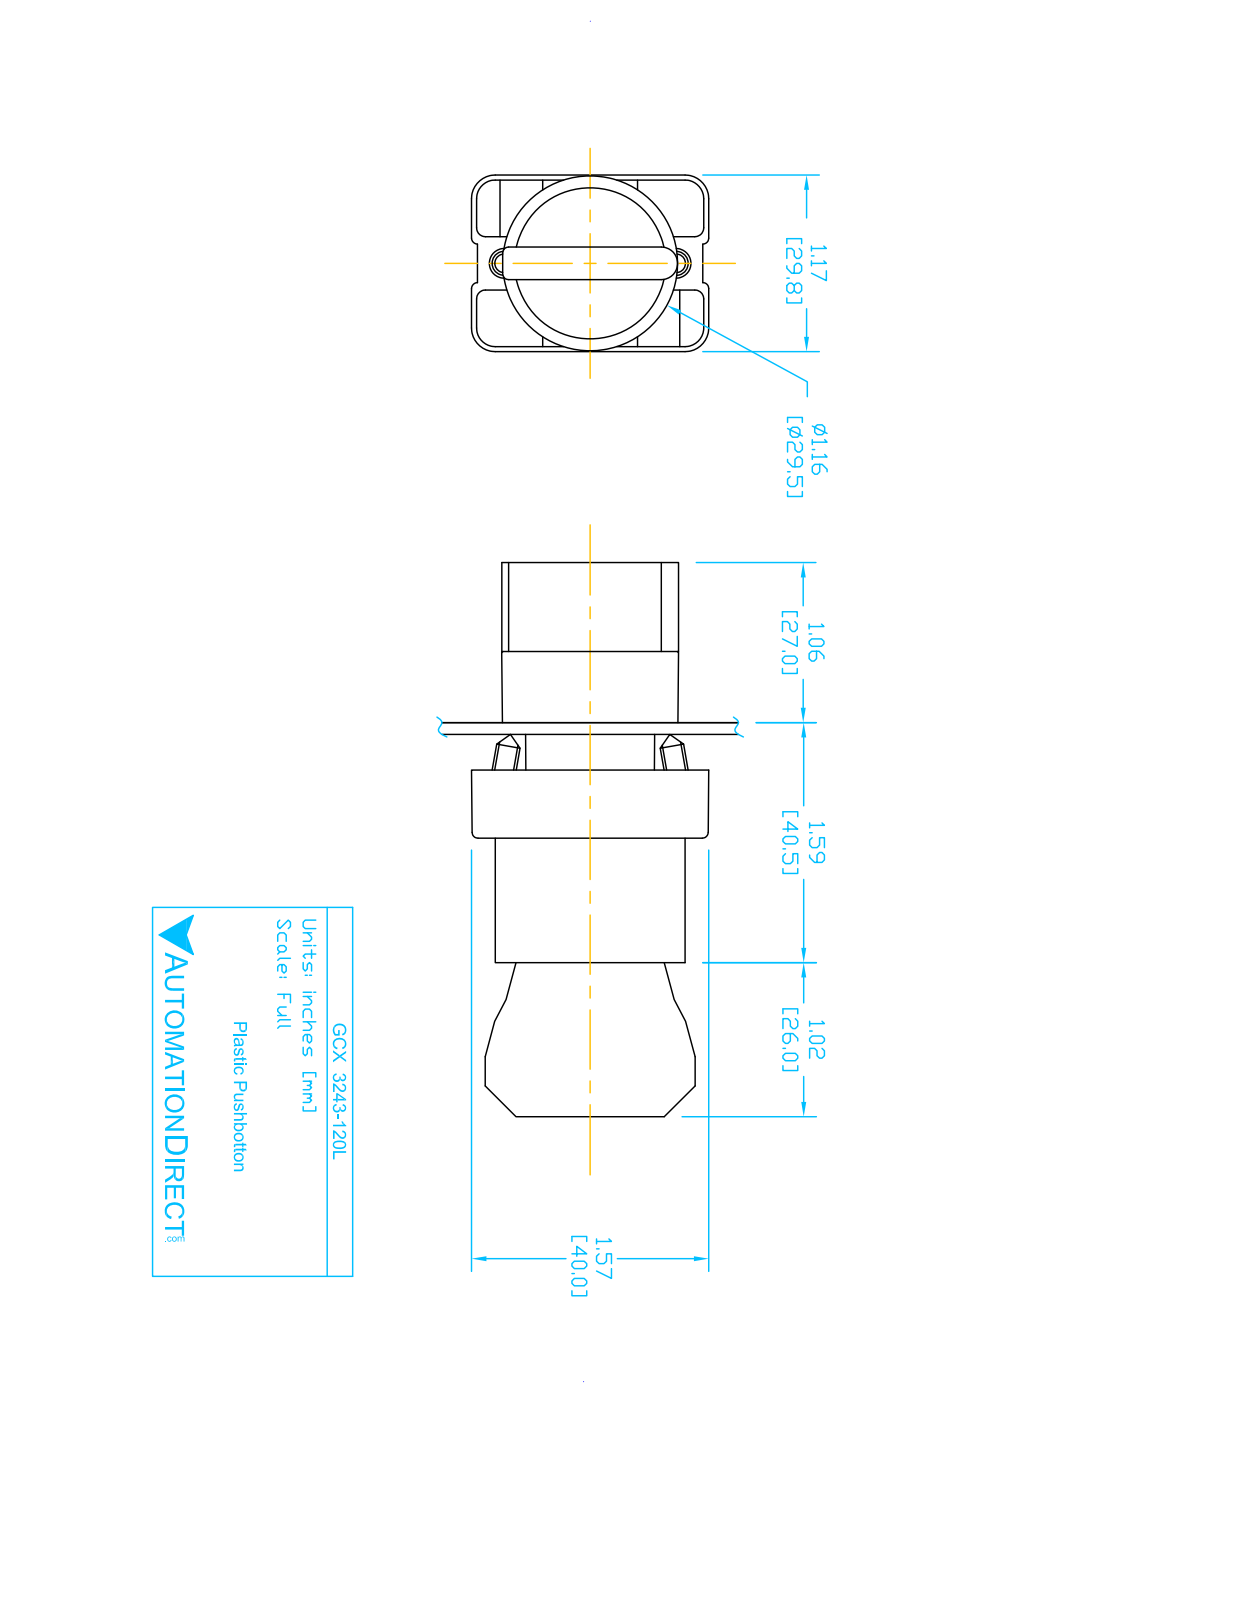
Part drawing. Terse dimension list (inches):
name: ecx1040; GCX3243-120L; GCX3243L OPERATOR; ECX3029-2 (+1 more)
written by: SolidWorks 2016 (AUTOMOTIVE_DESIGN)
unit: in
bodies: 8 solids, 445 faces (263 planar, 151 cylindrical, 31 other)
size: 3.653 × 1.581 × 1.177
volume: 2.799 in³; area: 39 in²
holes: 2× ⌀0.079, 2× ⌀0.124, 2× ⌀0.13, 1× ⌀0.087, 1× ⌀0.197, 1× ⌀0.469, 1× ⌀0.878, 1× ⌀0.888, 1× ⌀1.024
bosses: 4× ⌀0.157, 1× ⌀1.175, 1× ⌀1.004, 1× ⌀0.945, 1× ⌀0.856, 1× ⌀0.78, 1× ⌀0.504
rounds: 24× R0.059, 12× R0.041, 12× R0.124, 12× R0.157, 9× R0.039, 2× R0.128, 1× R0.02, 1× R0.063
face distances: 0.827, 2.02, 1.193, 0.579, 1.244, 1.171, 0.472, 0.469, 0.031, 0.033
hole spacings: 0.236, 0.544, 0.472, 0.49
